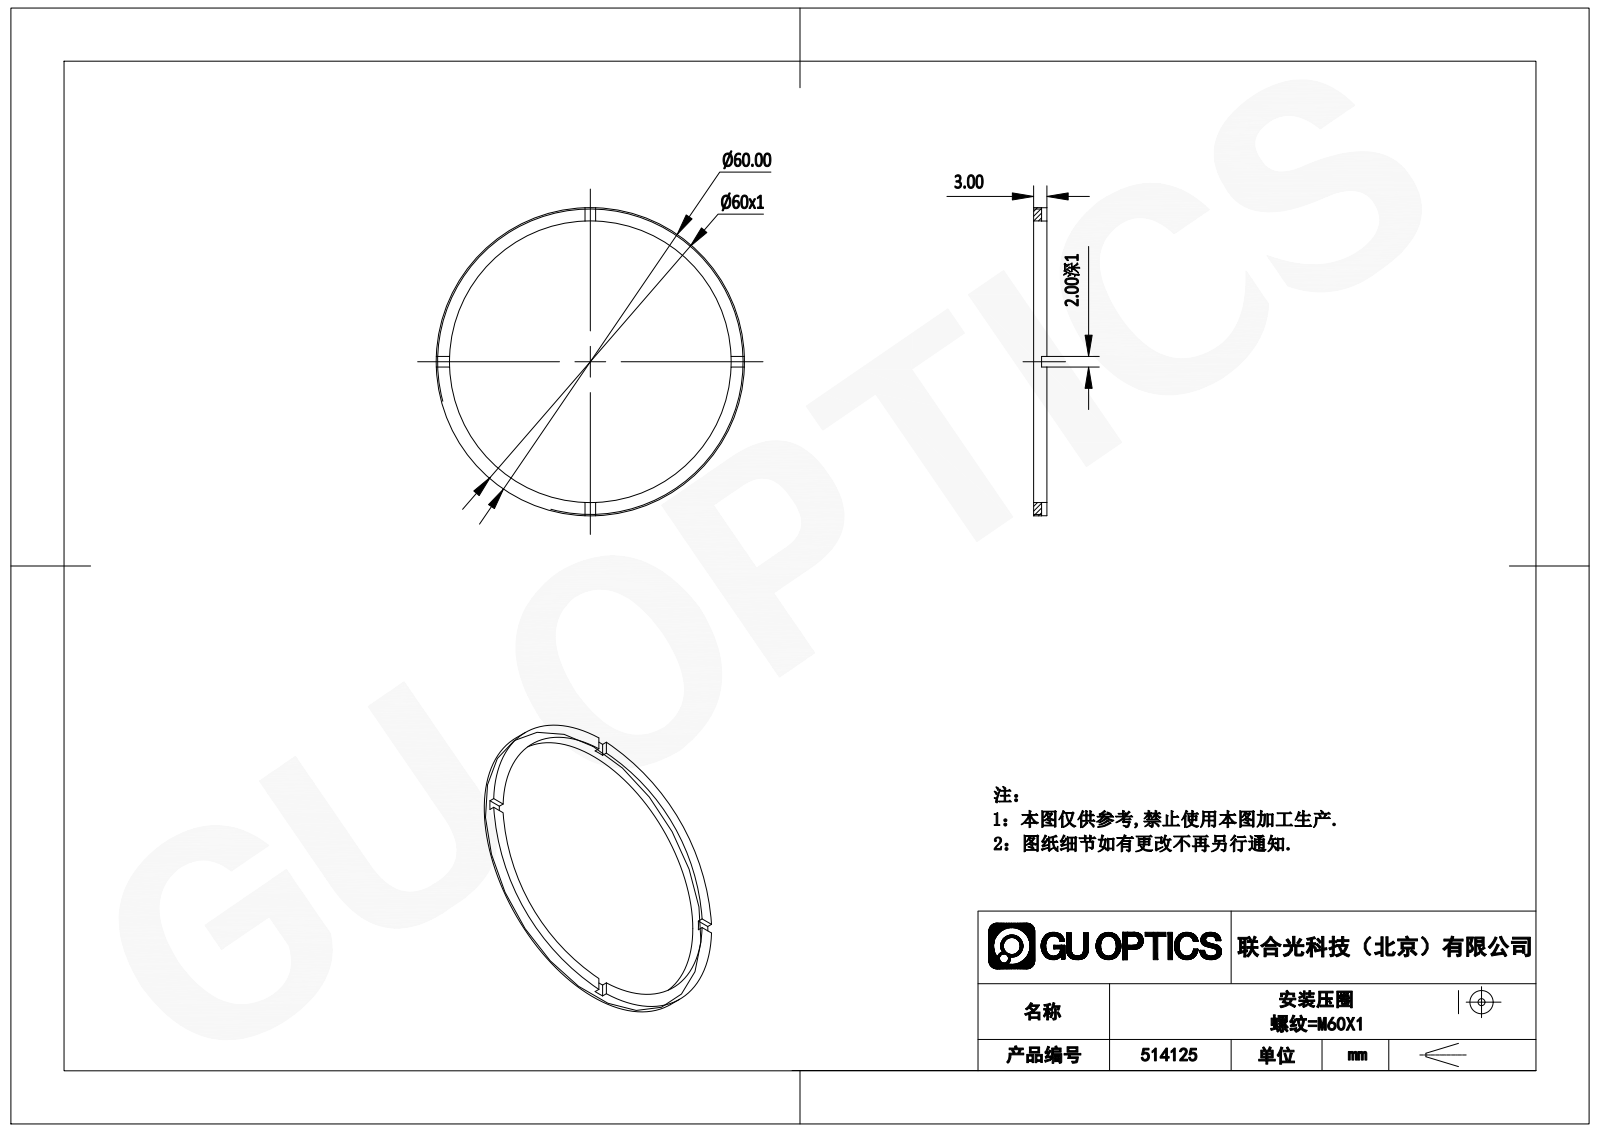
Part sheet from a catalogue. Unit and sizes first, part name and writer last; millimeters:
Units: millimetres
Overall size (bounding box): 60 × 60 × 3
Round holes (diameter × count): ⌀55 ×1
Round bosses / shafts (diameter × count): ⌀60 ×1
Main face-to-face distances: 3, 2, 1
Volume: 1 335 mm³ · Surface area: 1 991 mm²
Bodies: 1 solid, 21 faces (17 planar, 4 cylindrical, 0 other)
Part name (STEP PRODUCT): 514125
STEP written by: SolidWorks 2020 (CONFIG_CONTROL_DESIGN)
